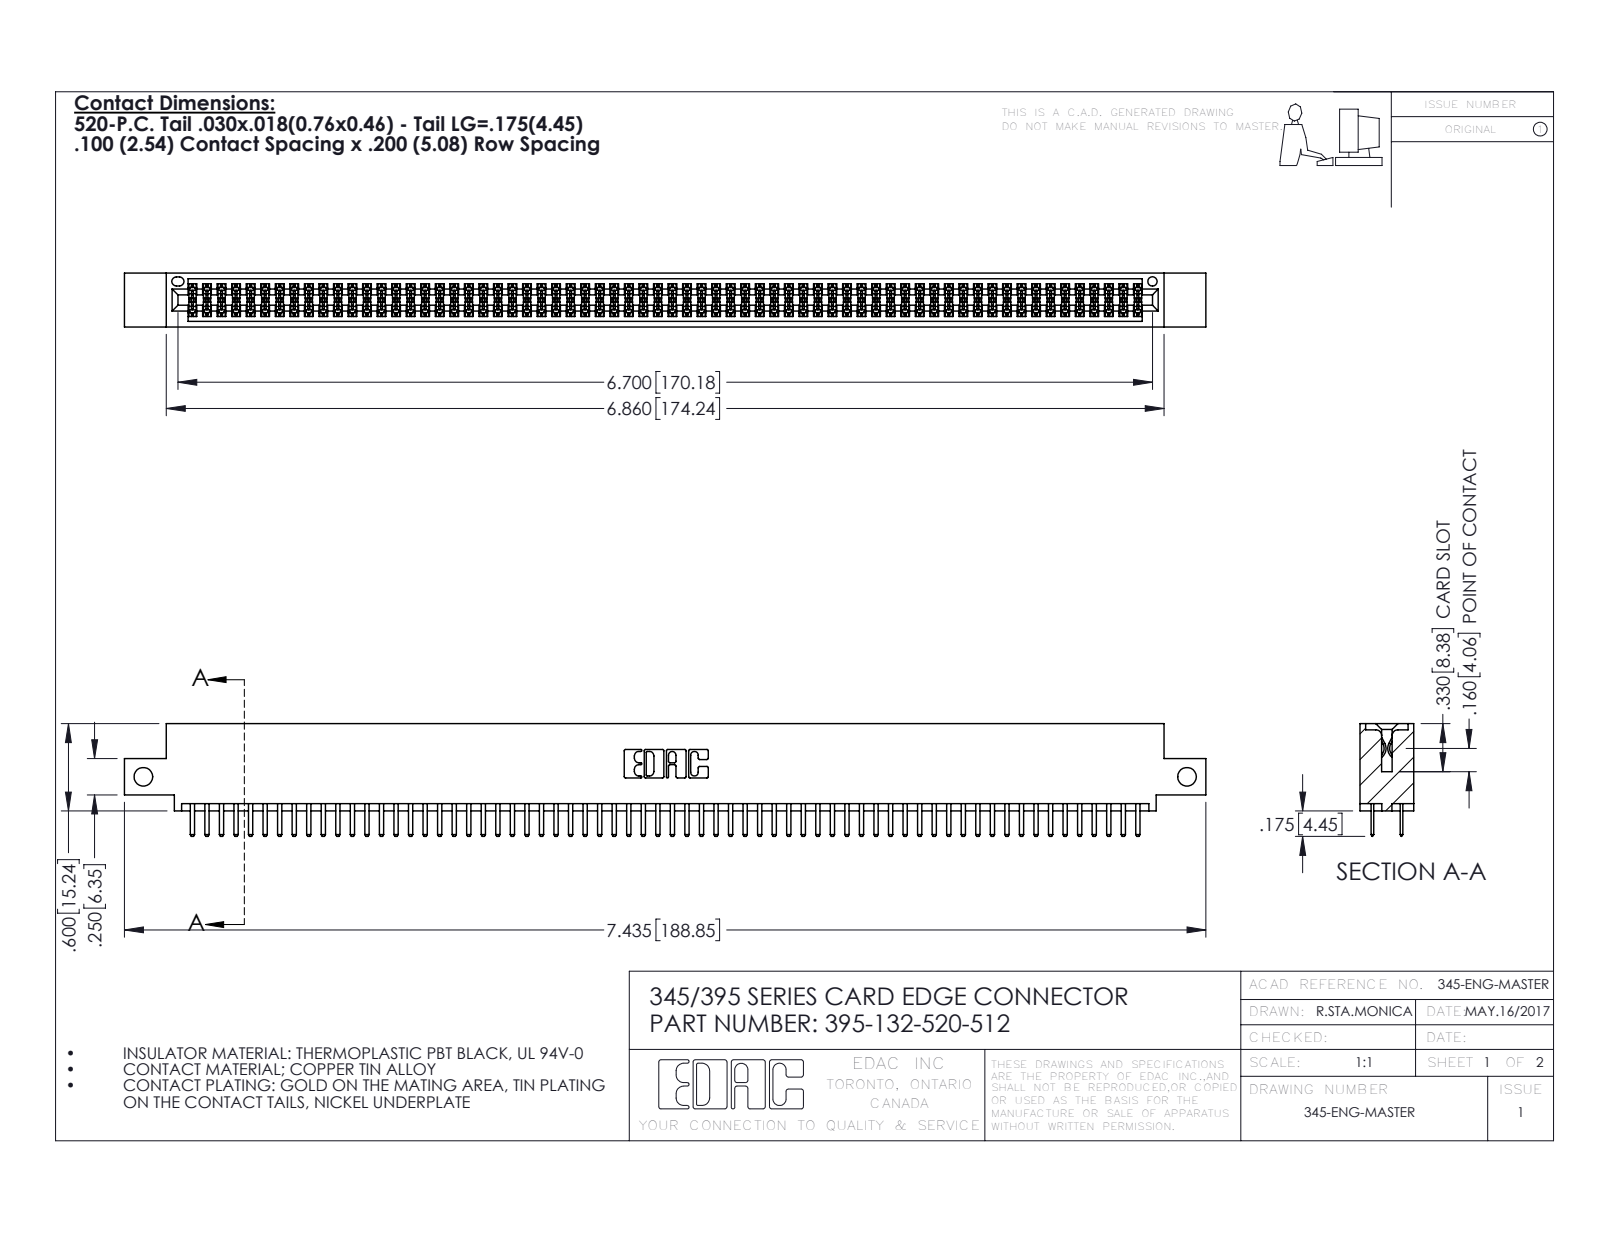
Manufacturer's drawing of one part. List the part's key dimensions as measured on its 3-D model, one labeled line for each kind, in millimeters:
Part name (STEP PRODUCT): 345 Part_0.110 Offset - Side Mount; 395-132-520-512; 345-292-001_345-293-120
STEP written by: SolidWorks 2016 (CONFIG_CONTROL_DESIGN)
Units: millimetres
Bodies: 133 solids, 7258 faces (4704 planar, 2554 cylindrical, 0 other)
Overall size (bounding box): 188.8 × 19.7 × 9.4
Volume: 18 350 mm³ · Surface area: 27 420 mm²
Round holes (diameter × count): ⌀3.3 ×2, ⌀1.6 ×1
Partial cylindrical surfaces — rounded edges, fillets, slot ends (radius × count): R0.2 ×198, R0.3 ×136, R0.3 ×22, R0.2 ×6, R0.8 ×6, R0.7 ×3, R0.4 ×2, R0.5 ×2
Main face-to-face distances: 7.6, 1.8, 5.1, 9.4, 2.5, 6.9, 0.6, 5.7, 0.6, 1.8
Hole centre spacings: 182.2
